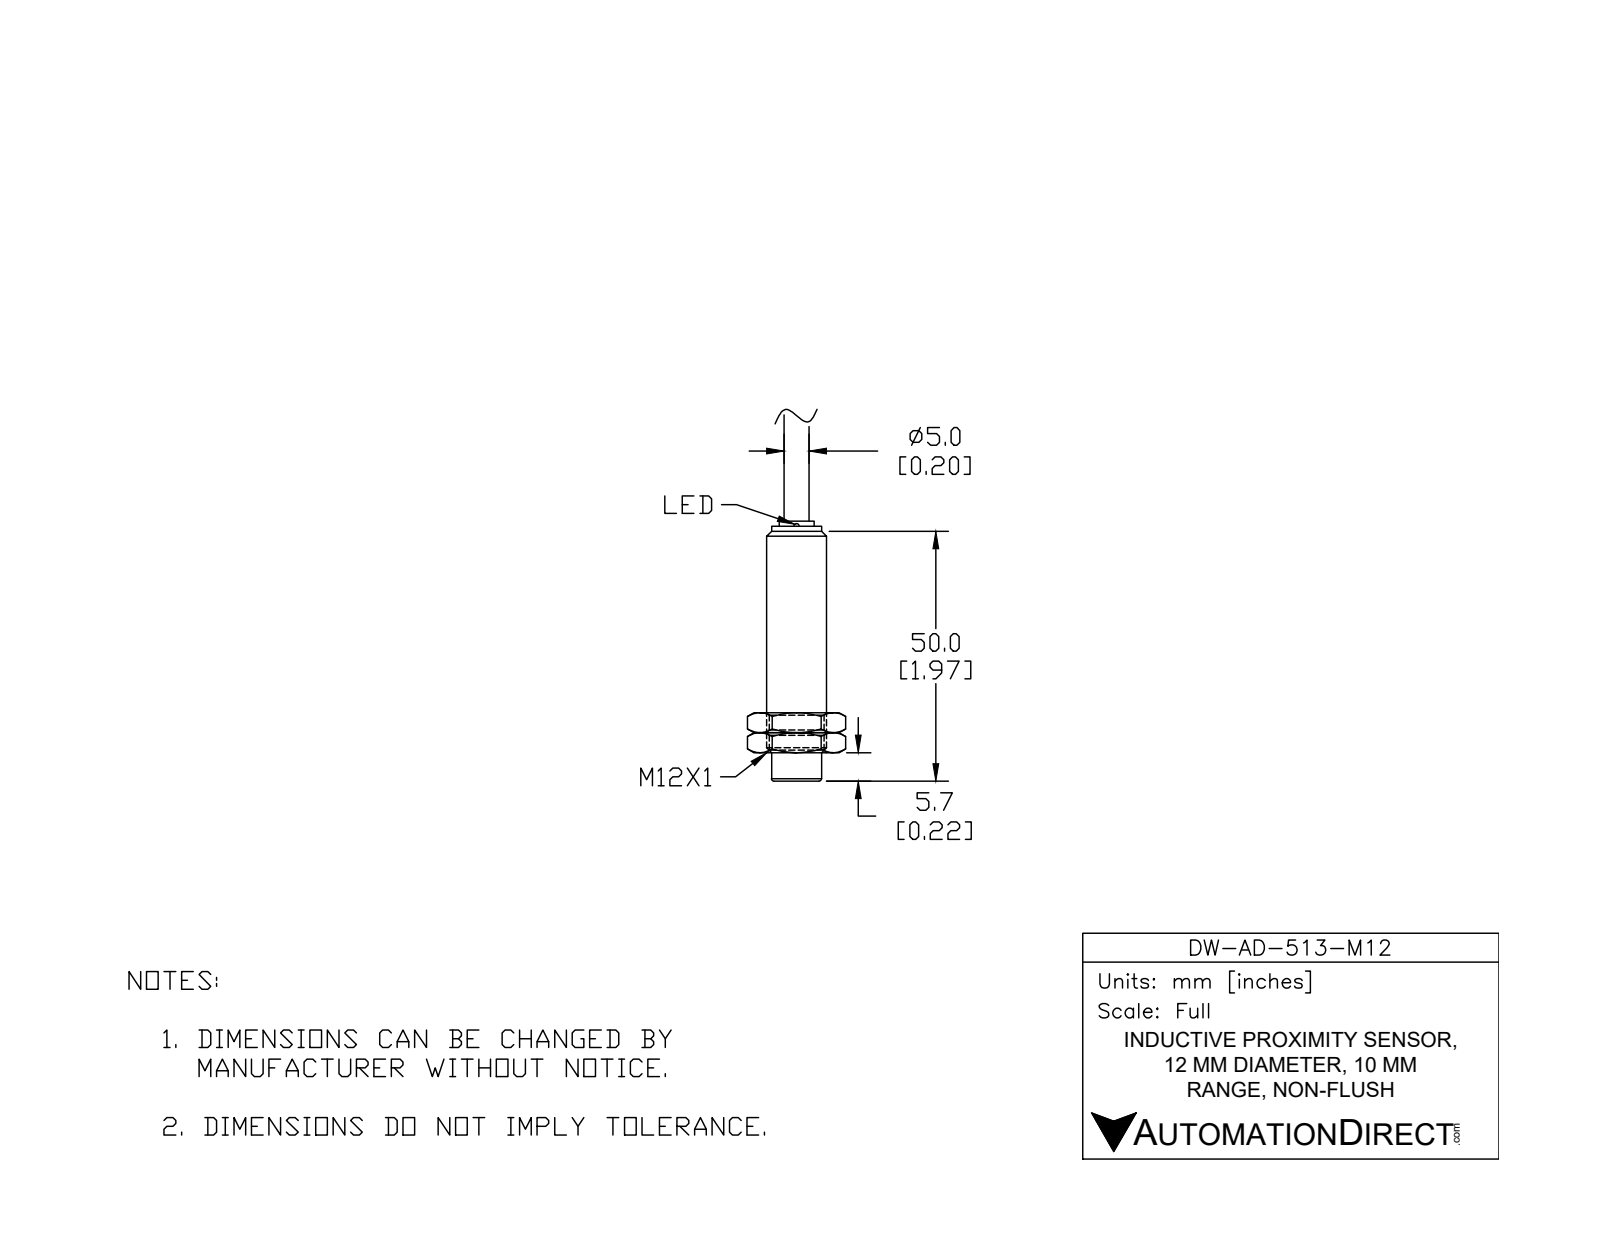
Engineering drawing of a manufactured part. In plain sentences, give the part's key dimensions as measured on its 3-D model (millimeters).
The part is named "DW-AD-513-M12". Its 3-D file was written by "SolidWorks 2017 (AUTOMOTIVE_DESIGN)". It is 1 solid with 30 faces: 15 planar, 5 cylindrical and 10 other. Overall it measures 75.6 by 12 by 12 millimeters. Its volume is 6 050 cubic millimeters and its surface area 2 451 square millimeters. Round bosses or shafts: 1 of diameter 12, 1 of diameter 10.7, 1 of diameter 10.5, 1 of diameter 6.8, 1 of diameter 5. The main face-to-face distances are 50.8, 52, 1.2, 51.6, 0.8, 0.4.
